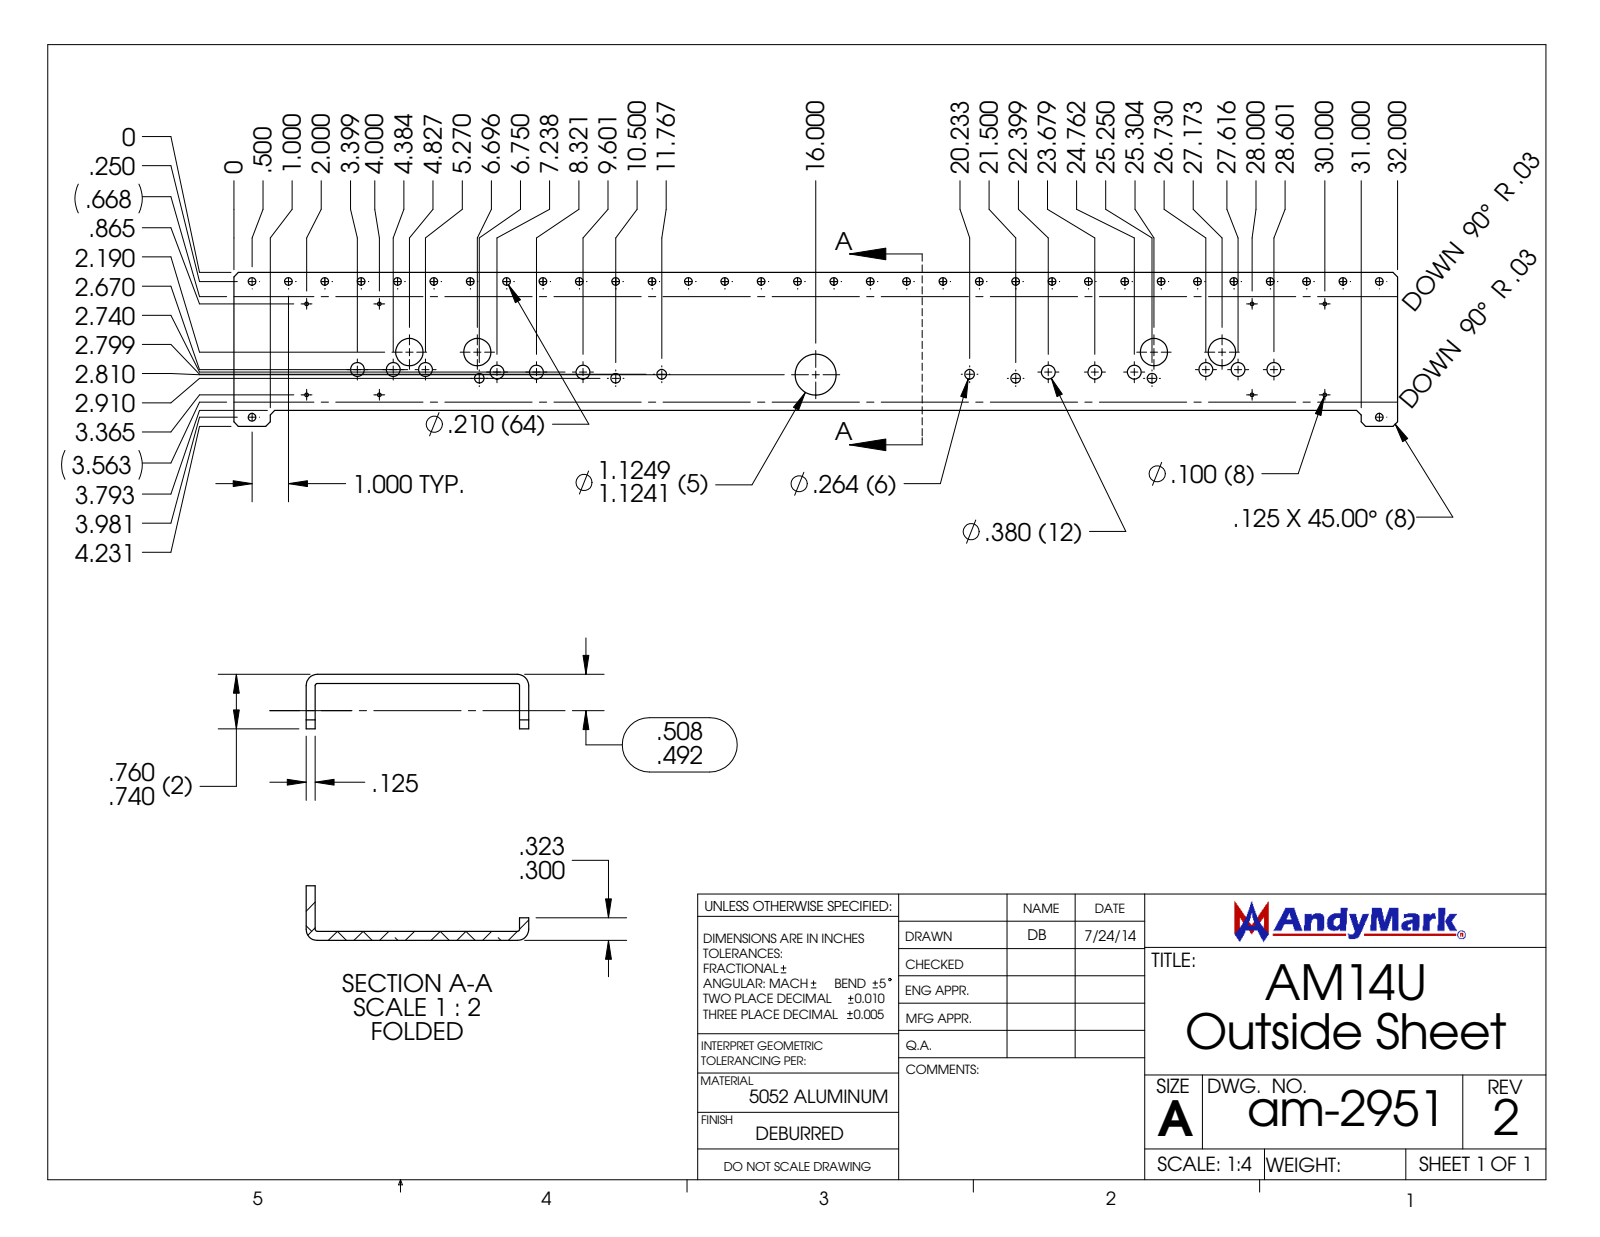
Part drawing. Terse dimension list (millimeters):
name: am-2951 AM14U2 Outside Sheet
written by: SolidWorks 2014 (AUTOMOTIVE_DESIGN)
unit: mm
bodies: 1 solid, 164 faces (30 planar, 134 cylindrical, 0 other)
size: 812.8 × 77.7 × 19.1
volume: 238 800 mm³; area: 160 800 mm²
holes: 32× ⌀5.3, 12× ⌀9.7, 8× ⌀2.5, 6× ⌀6.7, 4× ⌀19.1, 1× ⌀28.6
rounds: 2× R0.8, 2× R3.9
face distances: 3.2, 3.2, 74.5, 71.4, 77.7, 15.9, 19.1, 11.1, 4.7, 7.9
hole spacings: 50.8, 25.4, 76.2, 101.6, 127, 152.4, 177.8, 203.2
